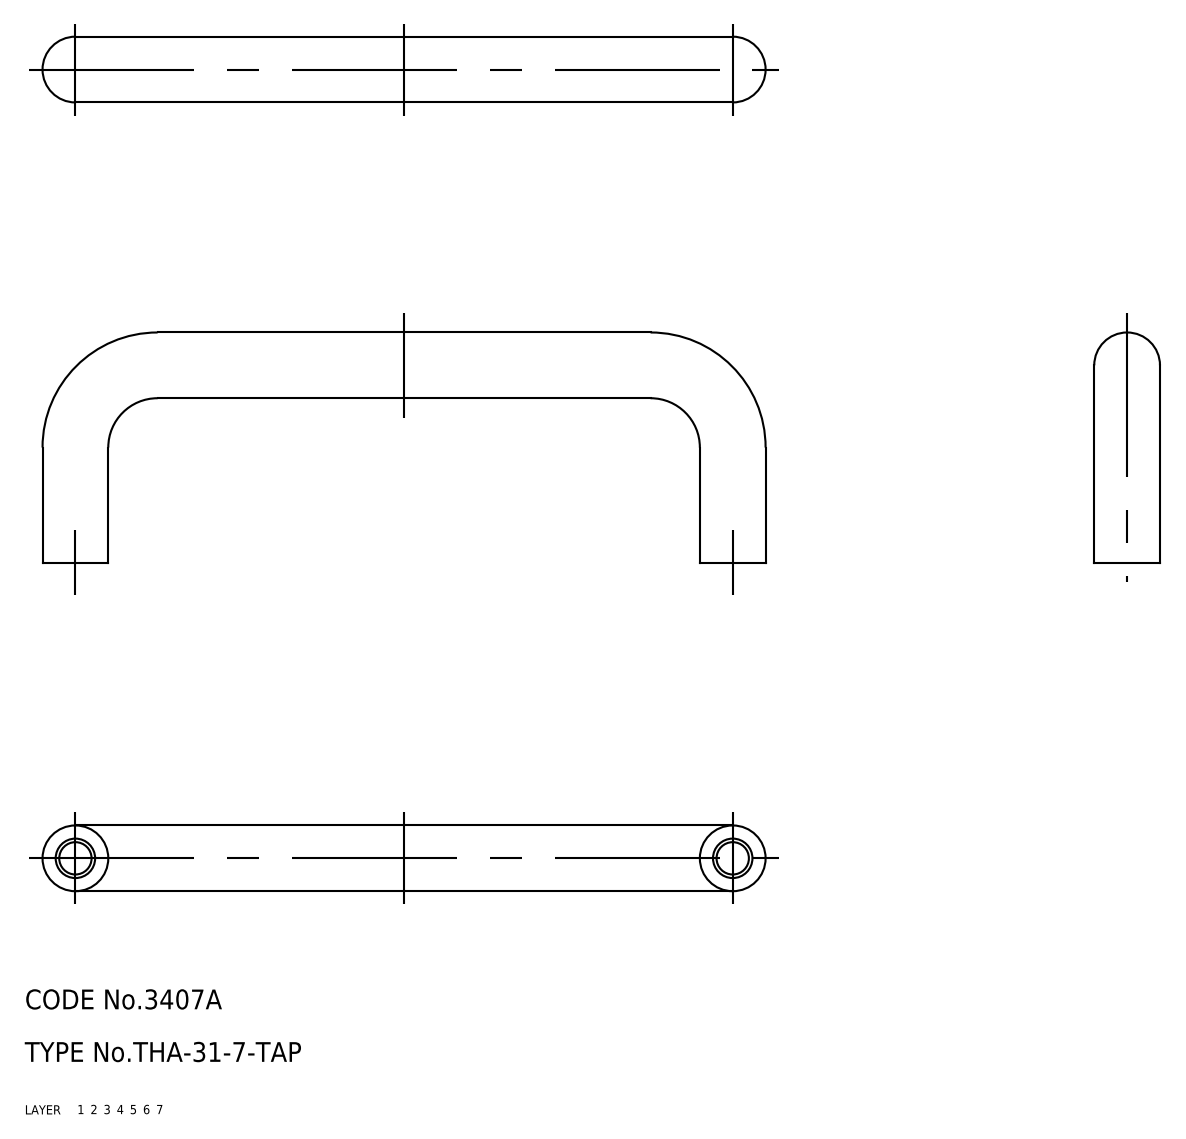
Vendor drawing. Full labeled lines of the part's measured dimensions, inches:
Part name (STEP PRODUCT): pull
STEP written by: CADfix (AUTOMOTIVE_DESIGN)
Units: inches
Bodies: 1 solid, 18 faces (0 planar, 0 cylindrical, 18 other)
Overall size (bounding box): 4.331 × 1.378 × 0.394
Volume: 0.662 in³ · Surface area: 8.452 in²
